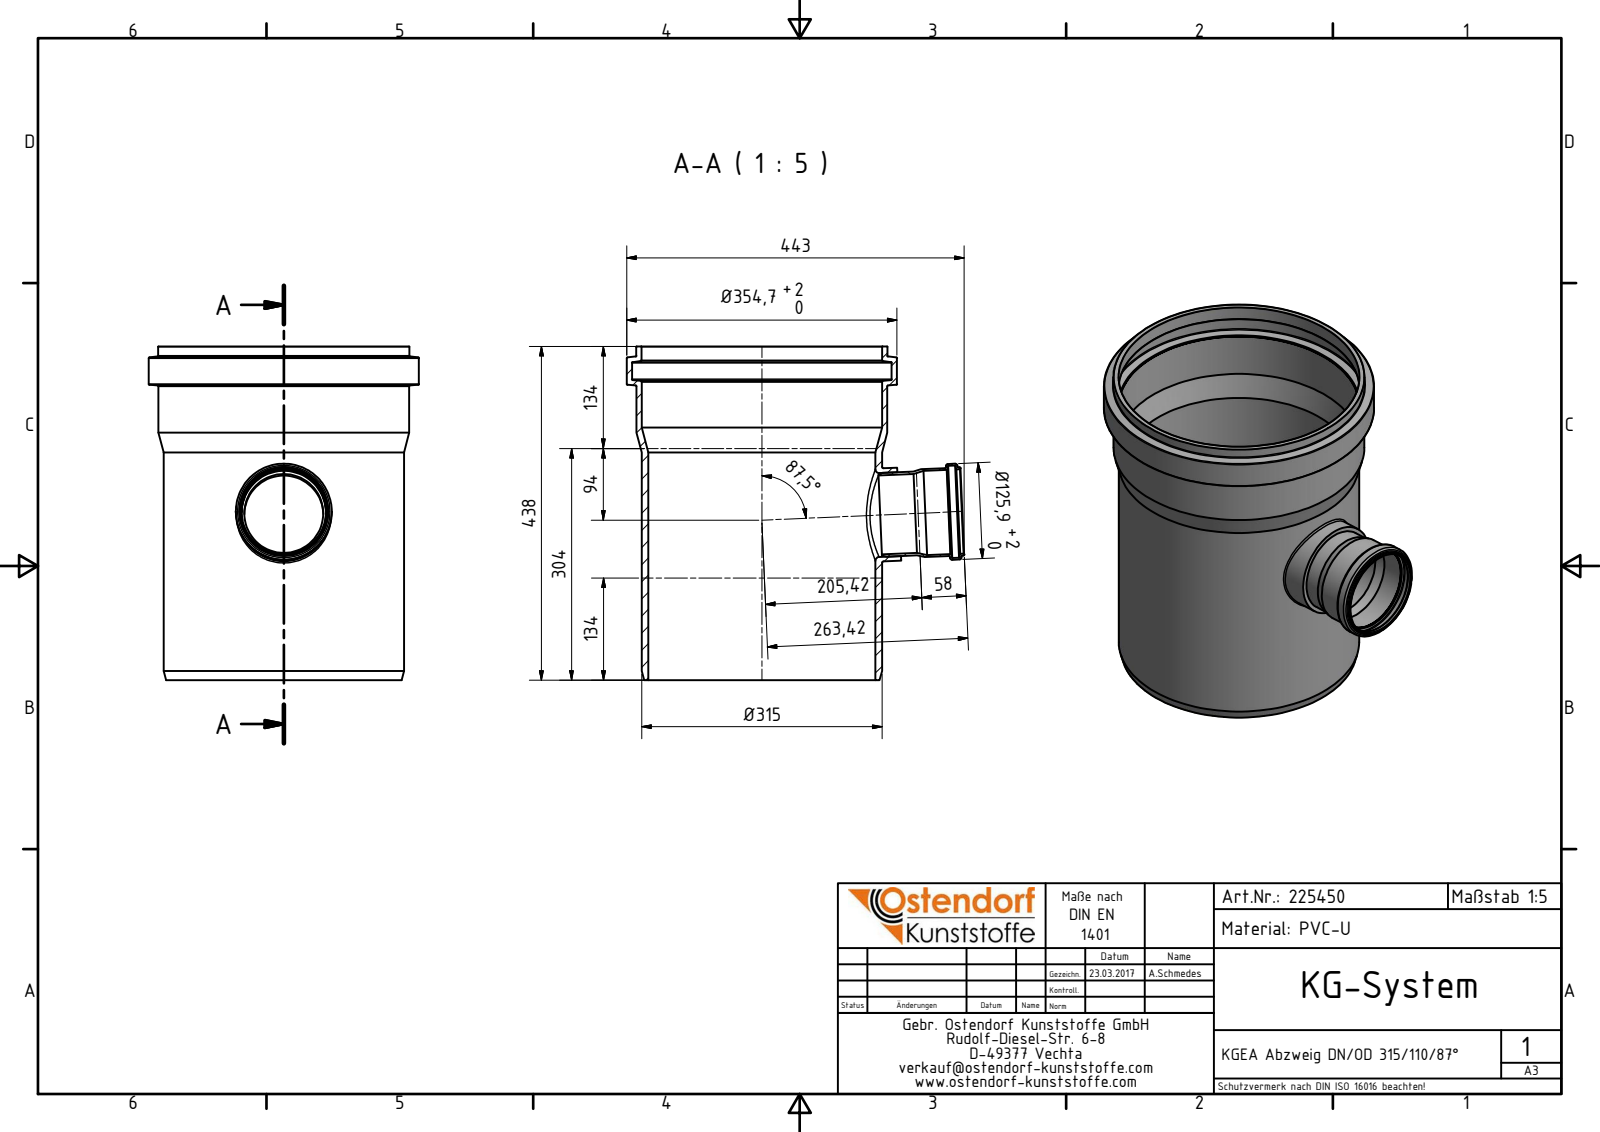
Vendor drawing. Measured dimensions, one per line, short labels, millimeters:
name: 225450 KGEA Abzweig DN_OD 315_110_87°; 225450 KGEA Abzweig DN_OD 315_110_87° Abzweig
written by: Autodesk Inventor 2016 (AUTOMOTIVE_DESIGN)
unit: mm
bodies: 2 solids, 63 faces (7 planar, 20 cylindrical, 36 other)
size: 443 × 438 × 354.7
volume: 3 777 000 mm³; area: 1 007 000 mm²
holes: 2× ⌀111, 1× ⌀103.6, 1× ⌀110, 1× ⌀110.7, 1× ⌀121.1, 1× ⌀298.2, 1× ⌀315.6, 1× ⌀315.9, 1× ⌀340.9
bosses: 1× ⌀354.7, 1× ⌀329.7, 1× ⌀329.4, 1× ⌀125.9, 1× ⌀122, 1× ⌀115.8, 1× ⌀115.5, 1× ⌀110
face distances: 438, 24.99, 391.44, 46.56, 107.83, 82.84, 89.63, 64.64, 18.2
